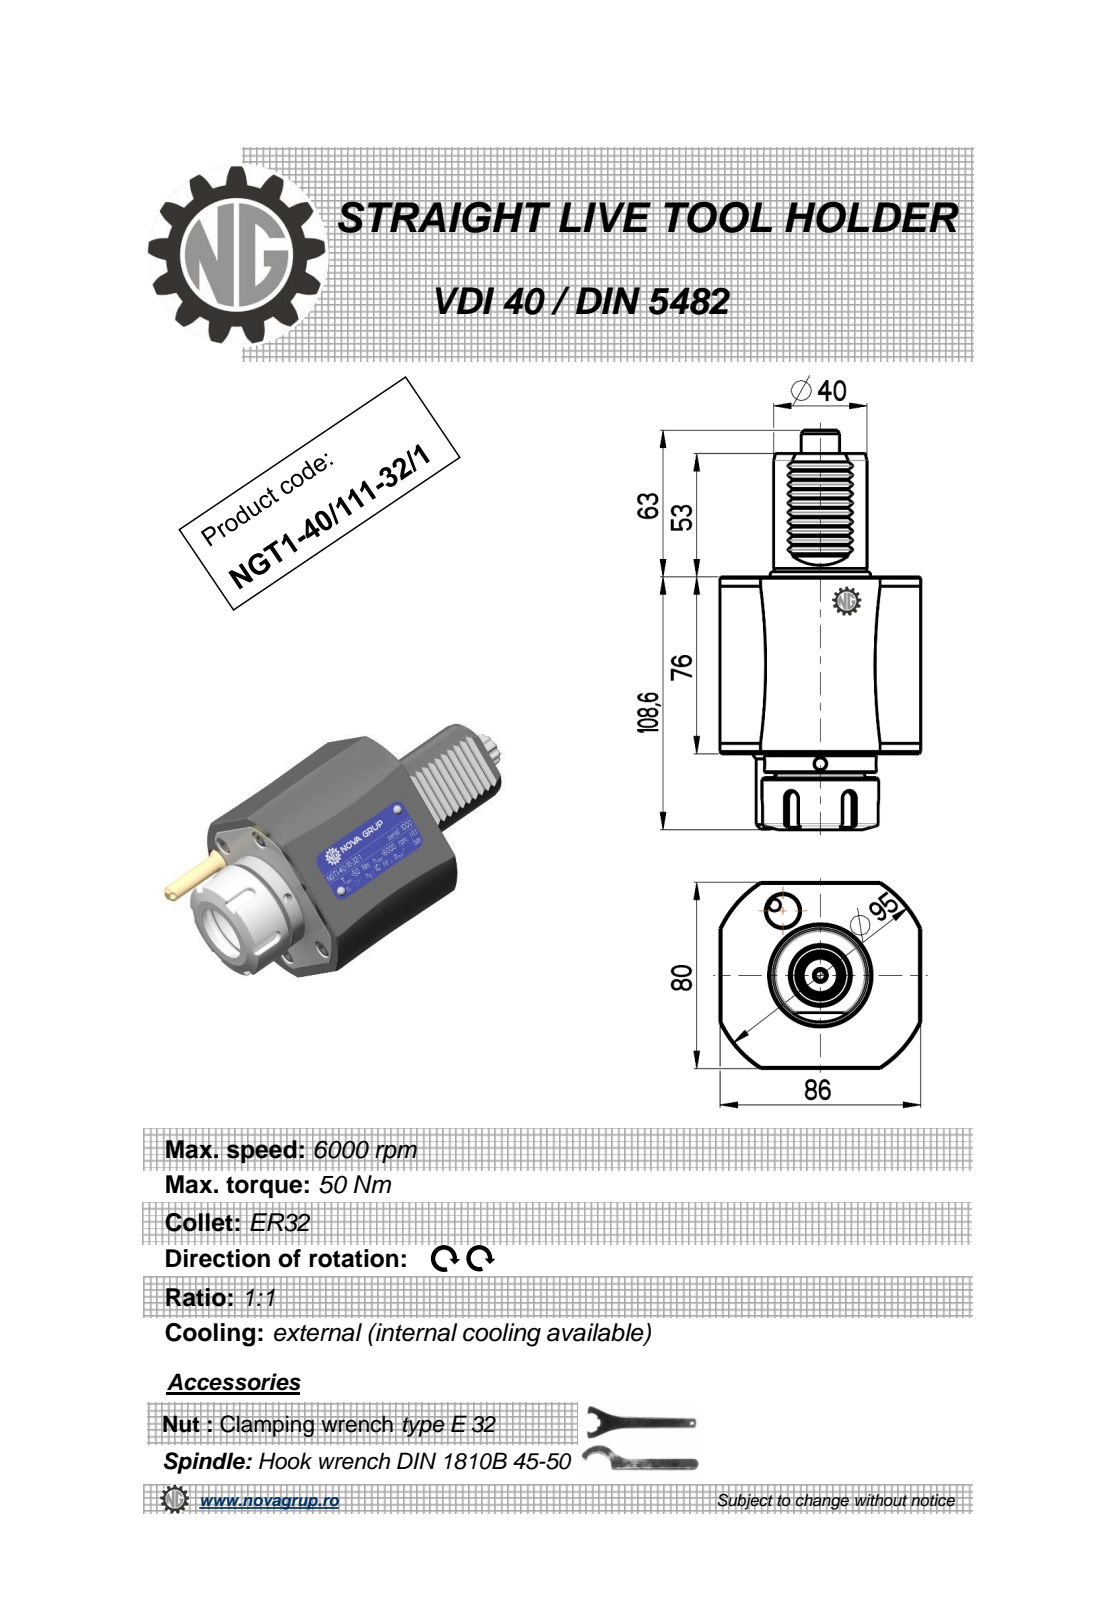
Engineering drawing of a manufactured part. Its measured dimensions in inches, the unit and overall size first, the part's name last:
Units: inches
Overall size (bounding box): 6.756 × 3.386 × 3.213
Round holes (diameter × count): ⌀0.197 ×3, ⌀0.118 ×1, ⌀0.165 ×1, ⌀1.063 ×1
Round bosses / shafts (diameter × count): ⌀1.969 ×1, ⌀1.89 ×1, ⌀1.634 ×1, ⌀1.614 ×1, ⌀1.575 ×1, ⌀0.315 ×1
Partial cylindrical surfaces — rounded edges, fillets, slot ends (radius × count): R0.119 ×18, R0.012 ×10, R0.009 ×6, R0.118 ×5, R0.266 ×1, R0.324 ×1, R1.87 ×1
Main face-to-face distances: 2.992, 3.15, 3.386, 2.087, 5.079, 0.111, 6.185, 4.098, 1.106, 0.223
Hole centre spacings: 1.575
Volume: 36.37 in³ · Surface area: 79.98 in²
Bodies: 1 solid, 297 faces (96 planar, 99 cylindrical, 102 other)
Part name (STEP PRODUCT): NGT1_40_111_32_1
STEP written by: PRO/ENGINEER BY PARAMETRIC TECHNOLOGY CORPORATION, 2010280 (CONFIG_CONTROL_DESIGN)
